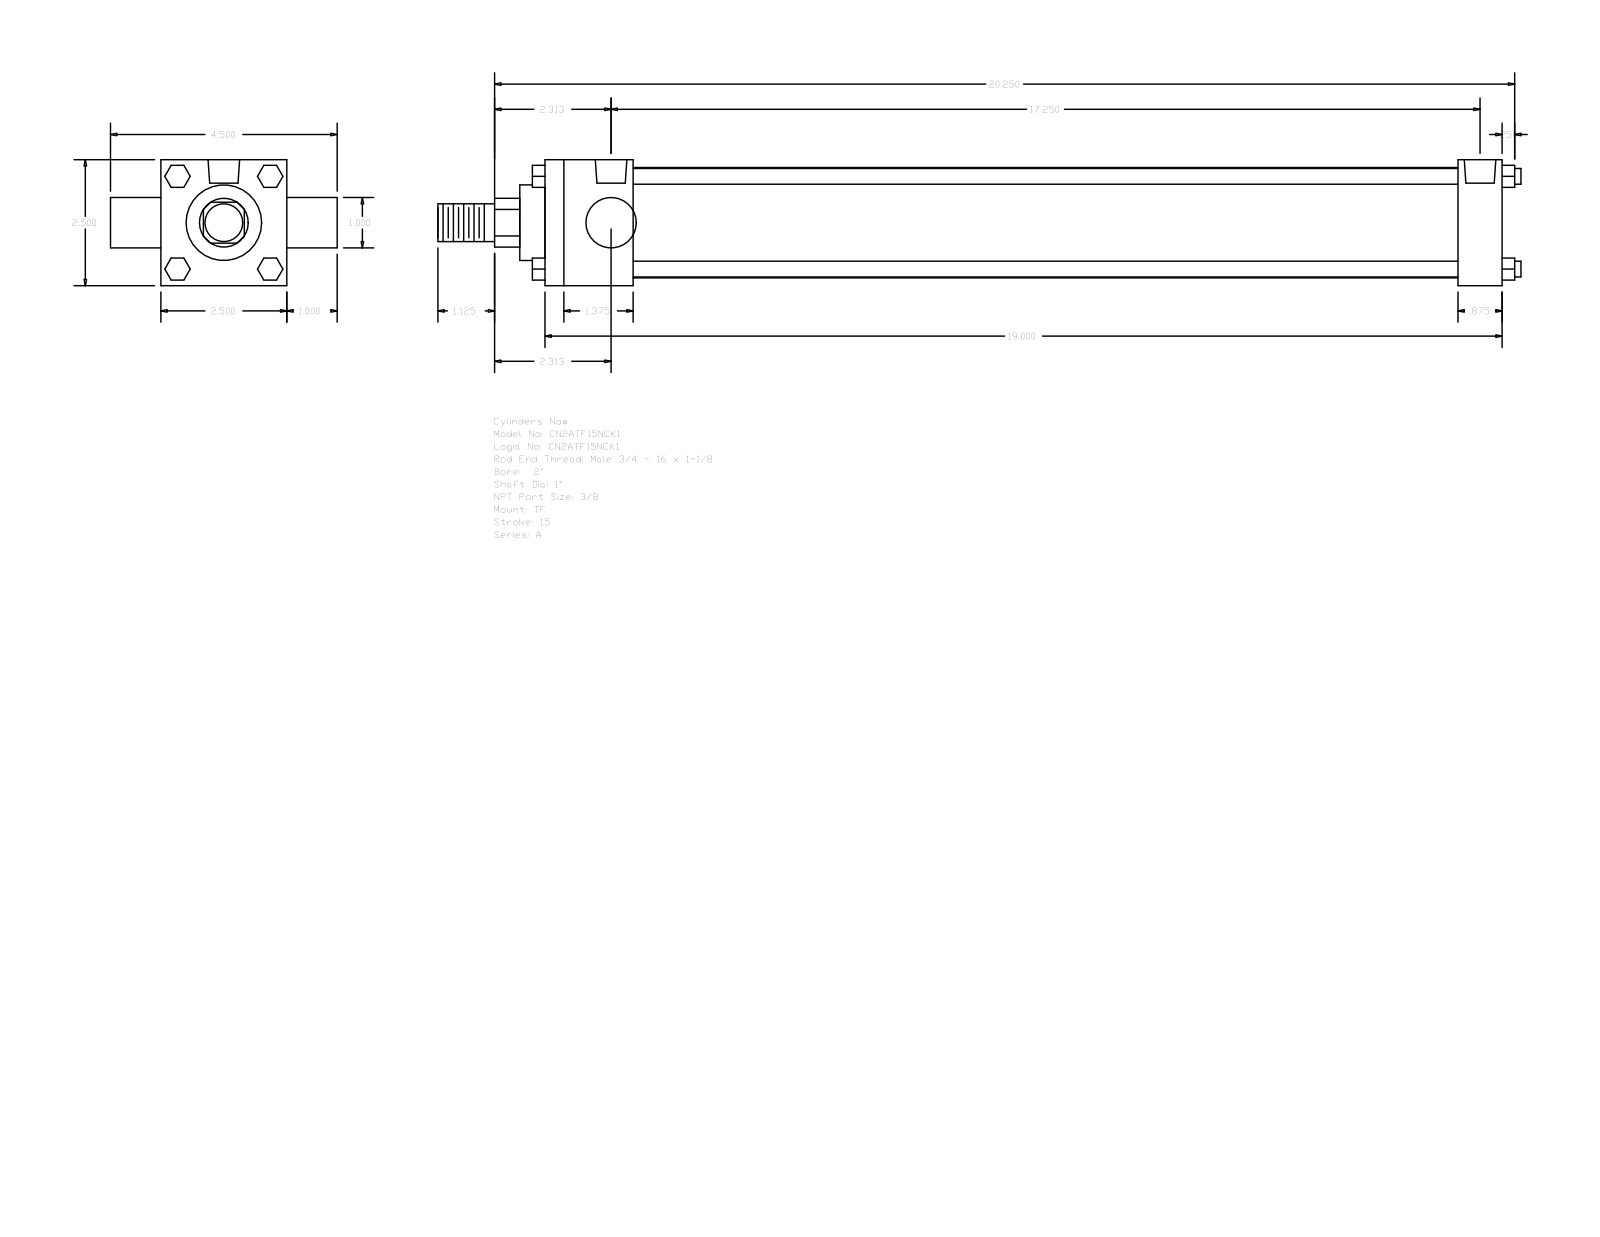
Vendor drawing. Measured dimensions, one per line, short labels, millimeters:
name: A_TF__0200_1
written by: GSSL Pune (CONFIG_CONTROL_DESIGN)
unit: mm
bodies: 0 solids, 120 faces (92 planar, 28 cylindrical, 0 other)
size: 546.1 × 114.3 × 63.5
holes: 3× ⌀5.56, 2× ⌀15.93
bosses: 4× ⌀7.94, 2× ⌀25.4, 1× ⌀55.63, 1× ⌀38.1, 1× ⌀19.05
rounds: 1× R12.29
face distances: 63.5, 482.6, 44.45, 460.37, 415.92, 438.15, 22.23, 25.4, 88.9, 495.3
hole spacings: 1.59, 3.98, 432.58, 434.17, 436.56, 438.15
